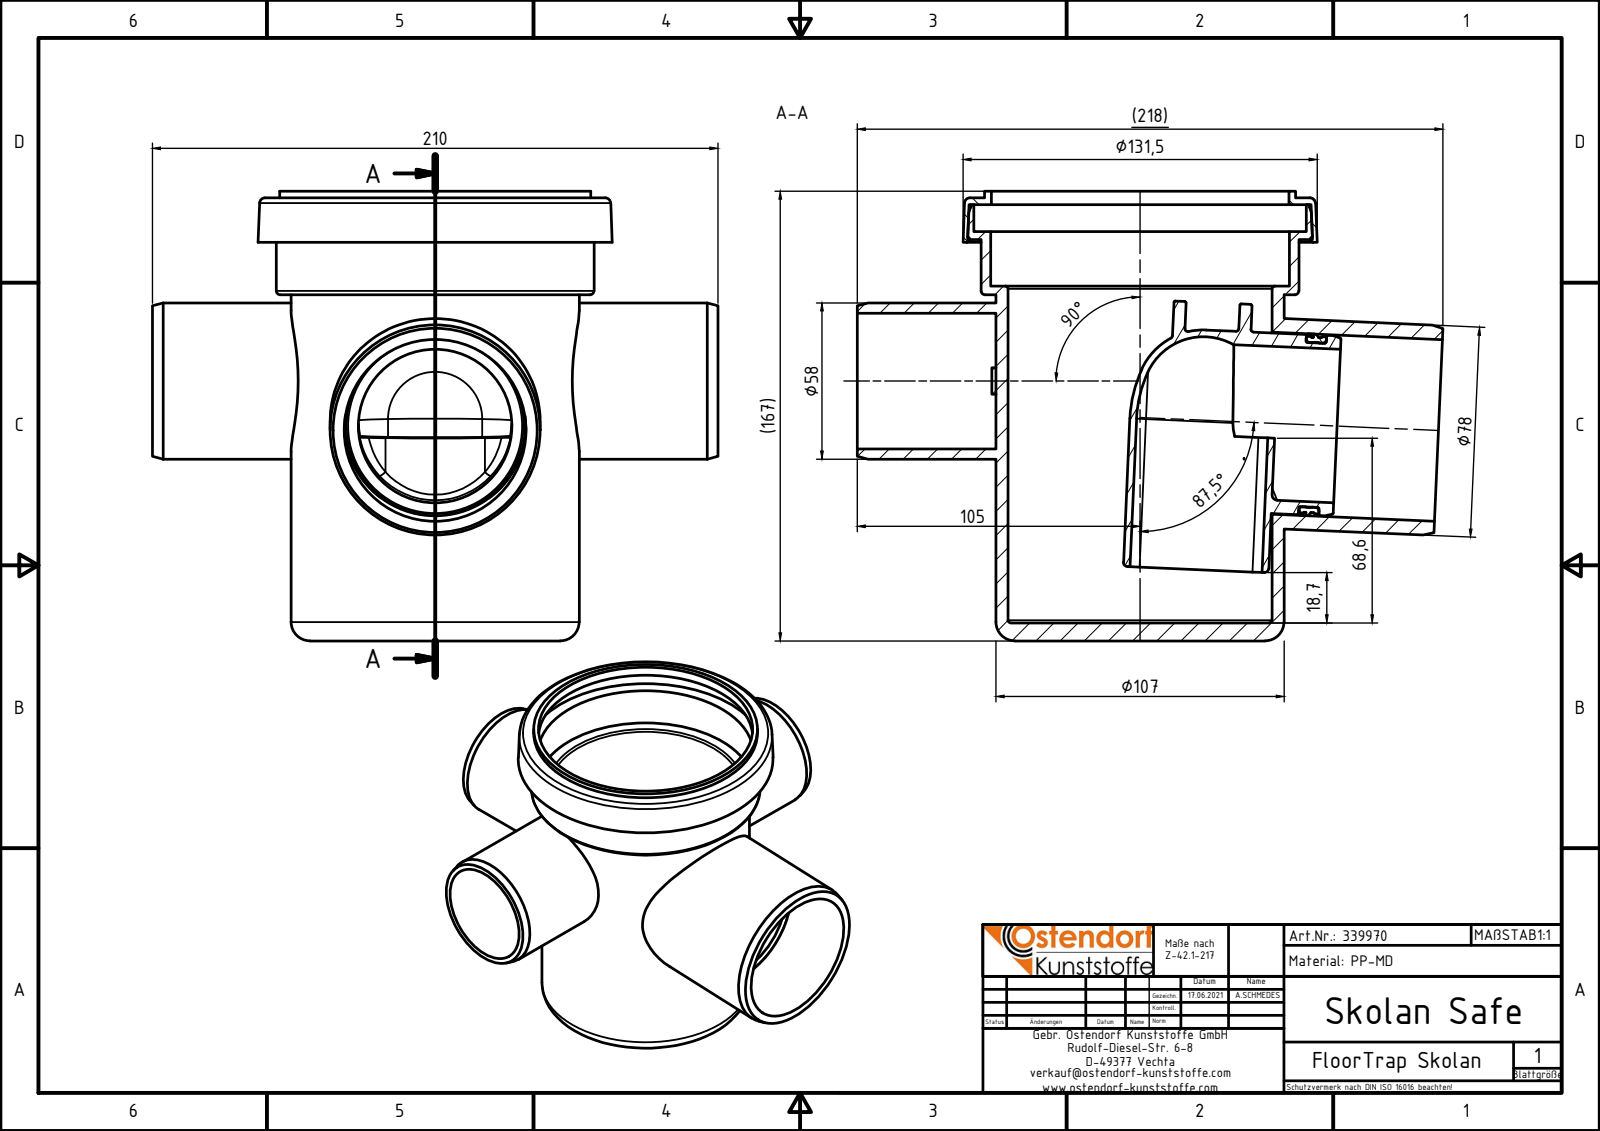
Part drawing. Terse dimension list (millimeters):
name: 339970 FloorTrap .idw; 339970 FloorTrap; 339970 FloorTrap Klickring; 339970 Floor Trap Einsatz
written by: Autodesk Inventor 2020 (AUTOMOTIVE_DESIGN)
unit: mm
bodies: 5 solids, 179 faces (41 planar, 64 cylindrical, 74 other)
size: 217.45 × 210 × 192.7
volume: 546 438 mm³; area: 281 992 mm²
holes: 2× ⌀50.4, 1× ⌀57, 1× ⌀61, 1× ⌀65.8, 1× ⌀67.5, 1× ⌀98, 1× ⌀110.5, 1× ⌀110.9, 1× ⌀123.5, 1× ⌀126.5
bosses: 2× ⌀58, 2× ⌀9.8, 1× ⌀125.6, 1× ⌀118, 1× ⌀115.5, 1× ⌀107, 1× ⌀78, 1× ⌀67.5
rounds: 8× R0.5, 4× R5, 2× R1, 2× R22.75, 2× R25.25, 2× R43.75, 2× R45.5, 2× R48
face distances: 6.7, 162, 155.3, 2.5, 152, 145.3, 10, 164.5, 157.8, 12.5
